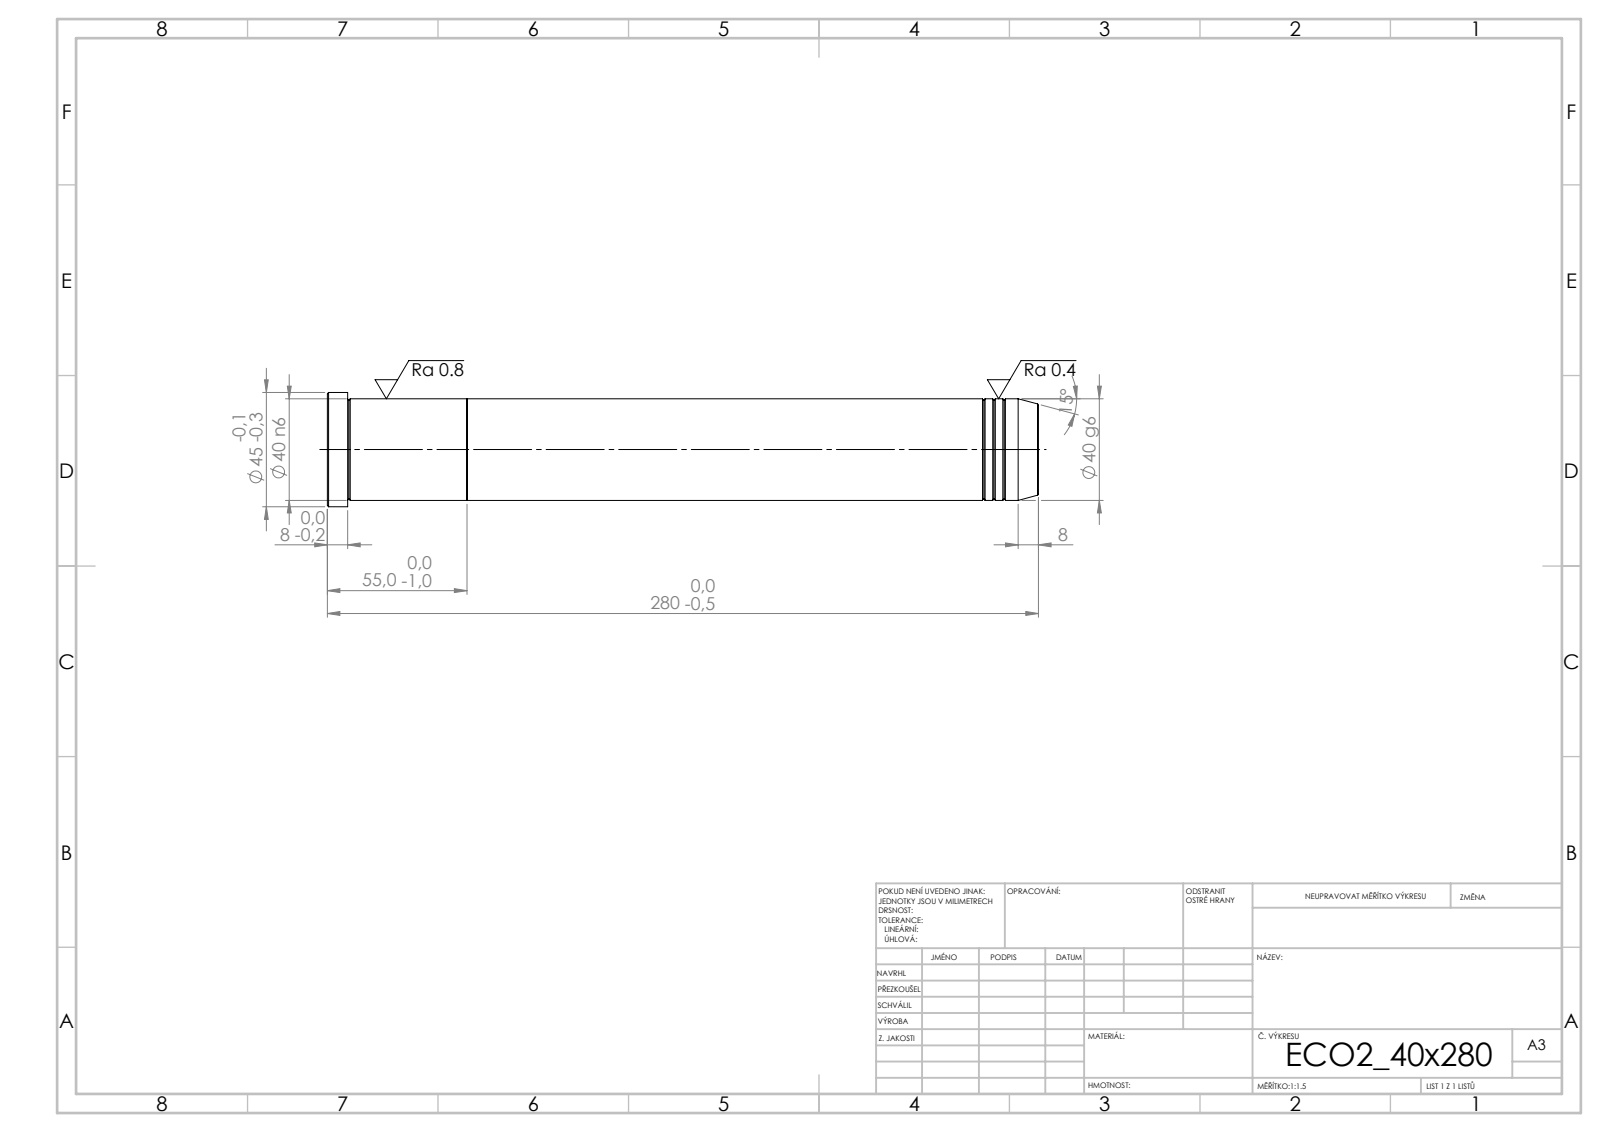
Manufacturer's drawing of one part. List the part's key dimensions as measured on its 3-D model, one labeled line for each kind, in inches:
STEP written by: SolidWorks 2019 (CONFIG_CONTROL_DESIGN)
Units: inches
Bodies: 2 solids, 39 faces (5 planar, 12 cylindrical, 22 other)
Overall size (bounding box): 11.024 × 1.772 × 1.772
Volume: 21.56 in³ · Surface area: 63.47 in²
Round bosses / shafts (diameter × count): ⌀1.772 ×1, ⌀1.575 ×1
Main face-to-face distances: 2.165, 8.858, 11.024, 10.709, 1.85, 0.315
